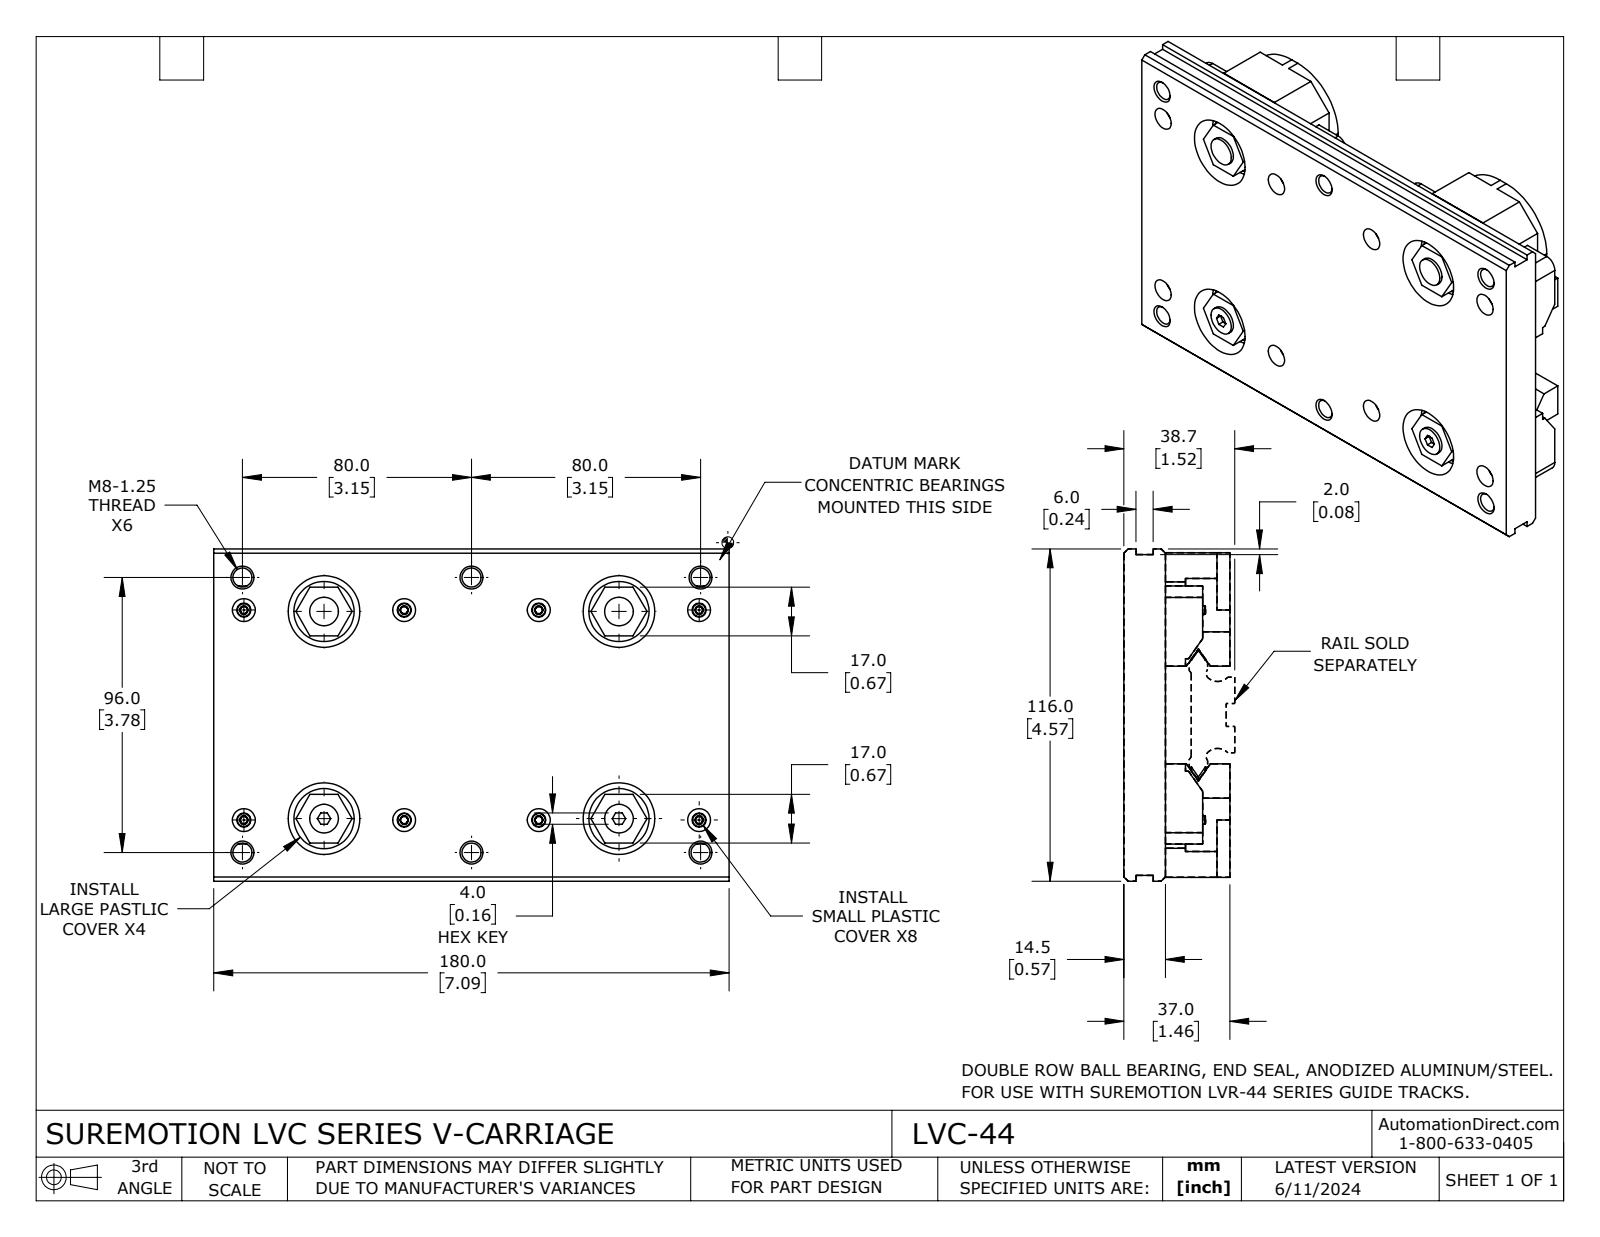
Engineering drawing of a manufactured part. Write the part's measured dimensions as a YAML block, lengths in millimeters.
part_name: "LVC-44"
step_written_by: "SolidWorks 2023 (CONFIG_CONTROL_DESIGN)"
units: millimeters
bodies: {solids: 17, faces: 784, planar: 396, cylindrical: 188, other: 200}
overall_size: [180, 116, 37]
volume: 527832
surface_area: 119625
round_holes:
  - {diameter: 2.85, count: 8}
  - {diameter: 4.5, count: 8}
  - {diameter: 8, count: 8}
  - {diameter: 6.65, count: 6}
  - {diameter: 3.24, count: 4}
  - {diameter: 25, count: 4}
round_bosses_or_shafts:
  - {diameter: 5.5, count: 8}
  - {diameter: 3, count: 8}
  - {diameter: 34, count: 4}
  - {diameter: 21, count: 4}
  - {diameter: 12, count: 4}
  - {diameter: 10, count: 4}
partial_cylinders:
  - {radius: 4, count: 8}
  - {radius: 5, count: 8}
  - {radius: 20, count: 8}
face_to_face_distances: [14.5, 37, 22.5, 2, 17, 2.5, 5.5, 8, 35, 28]
hole_center_spacings: [28, 78, 103, 11.21, 11.36, 18.4, 26.1, 30.87]
